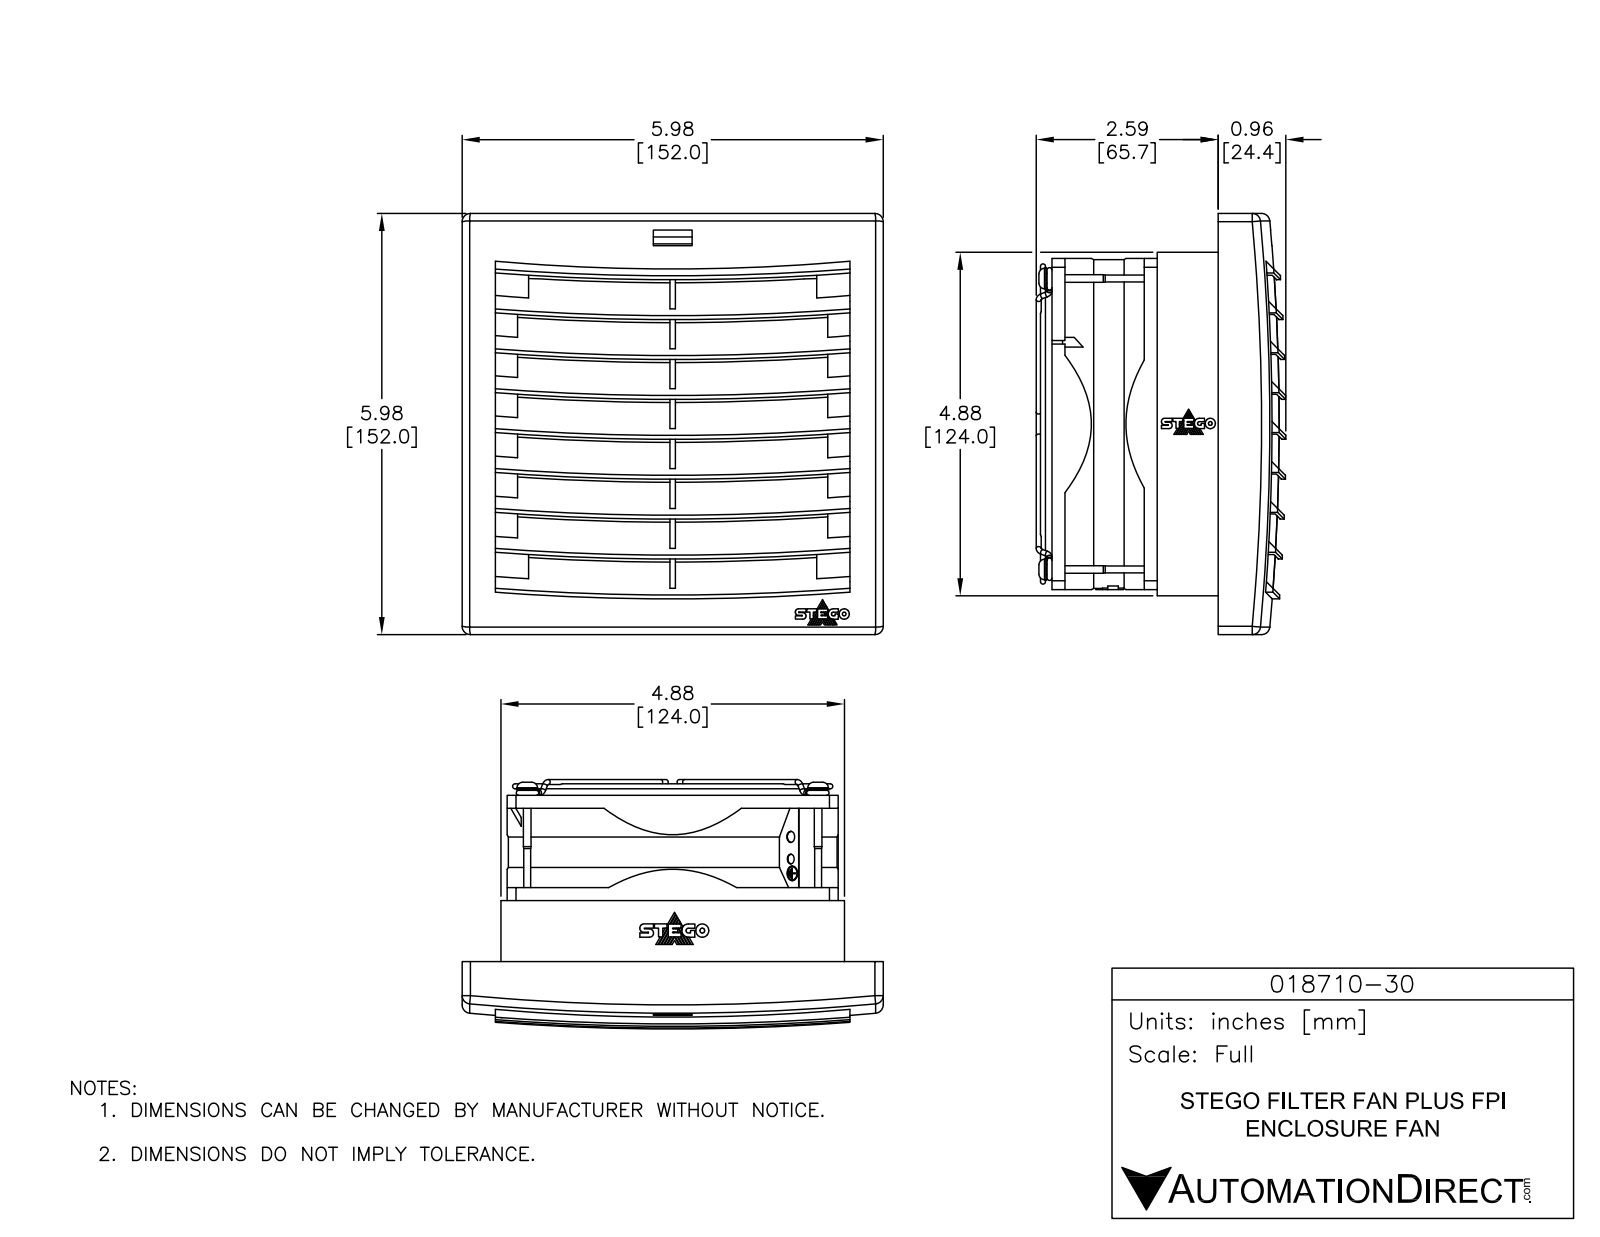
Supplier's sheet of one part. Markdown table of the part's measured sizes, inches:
| quantity | value |
| --- | --- |
| part name | 018710-30_NEW |
| STEP written by | SolidWorks 2018 (AUTOMOTIVE_DESIGN) |
| units | inches |
| bodies | 13 solids, 521 faces (249 planar, 162 cylindrical, 110 other) |
| overall size | 5.984 × 5.984 × 3.472 |
| volume | 49.35 in³ |
| surface area | 310 in² |
| round holes (diameter × count) | 4.397 × 1, 4.45 × 1 |
| round bosses / shafts (diameter × count) | 0.071 × 15, 0.307 × 4, 0.186 × 4, 4.672 × 1, 2.08 × 1 |
| partial cylindrical surfaces (radius × count) | 0.024 × 40, 0.006 × 20, 0.125 × 8, 0.057 × 4, 0.067 × 4, 0.11 × 4, 2.377 × 2, 30.822 × 2 |
| main face-to-face distances | 1.051, 0.797, 0.551, 5.433, 2.177, 1.126, 2.48, 0.398, 0.399, 1.196 |
